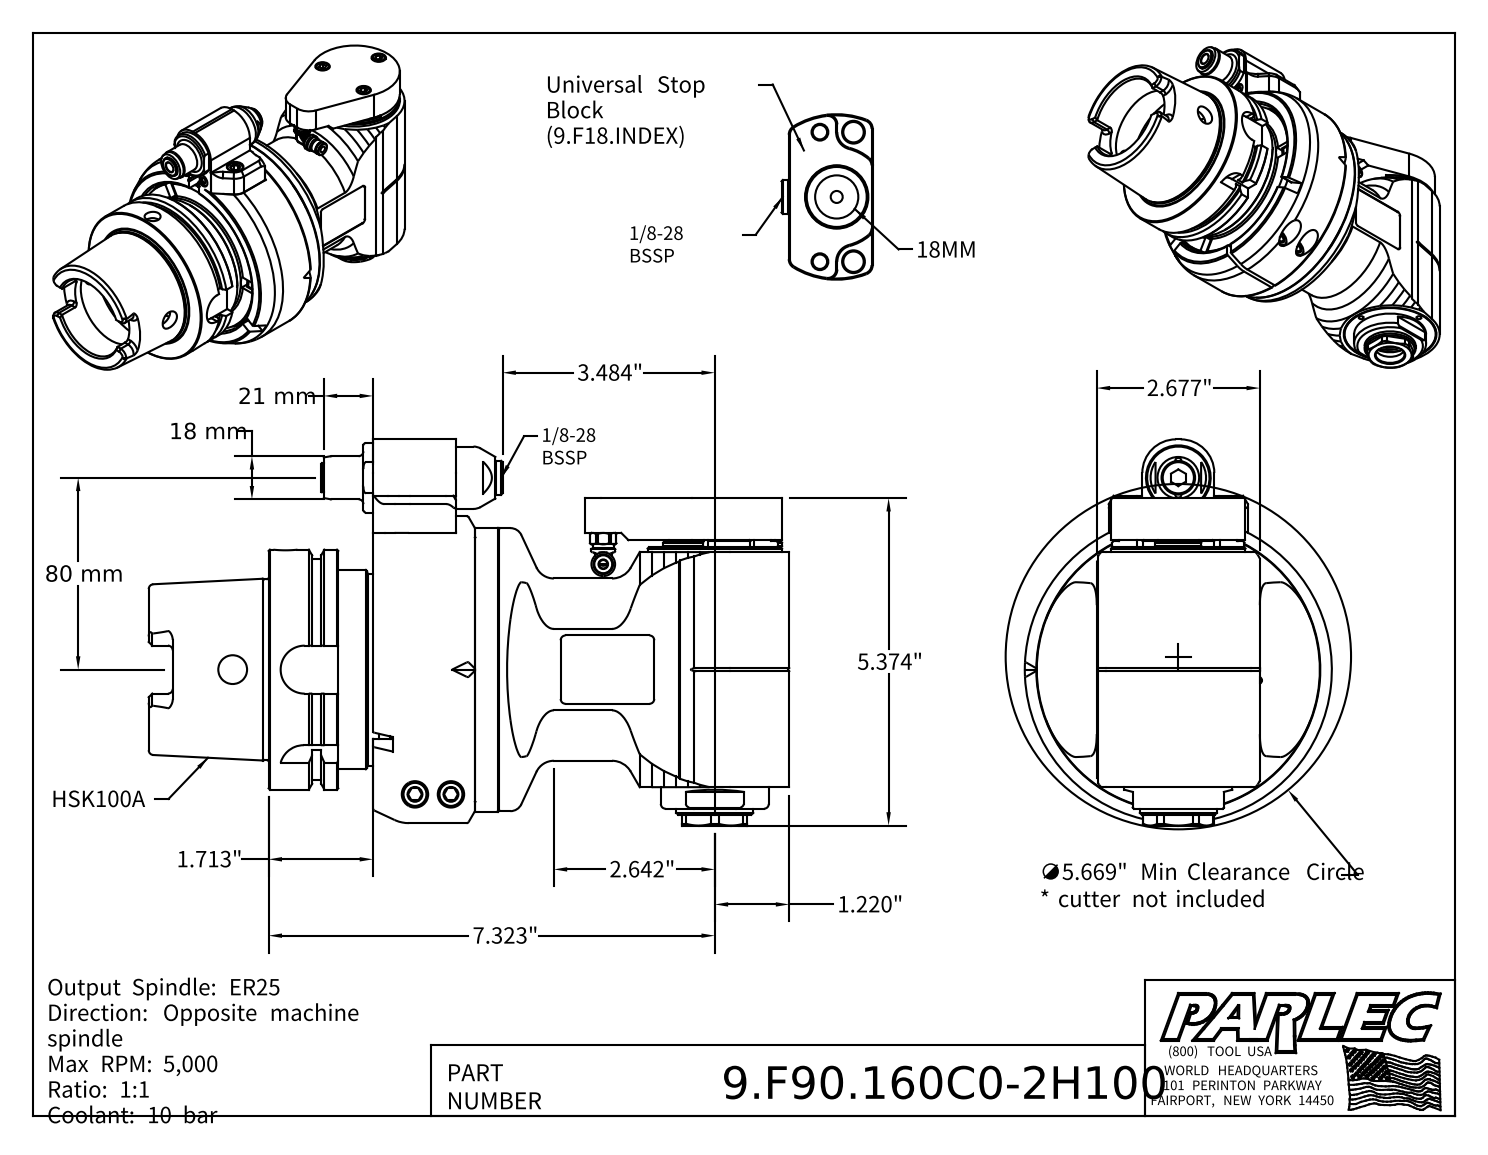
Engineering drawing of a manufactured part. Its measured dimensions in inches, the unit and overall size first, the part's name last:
Units: inches
Overall size (bounding box): 10.512 × 6.339 × 5.039
Round holes (diameter × count): ⌀0.413 ×20, ⌀0.126 ×4, ⌀0.197 ×3, ⌀0.256 ×3, ⌀0.354 ×3, ⌀0.492 ×3, ⌀0.102 ×2, ⌀0.13 ×2, ⌀0.138 ×2, ⌀0.165 ×2, ⌀0.315 ×2, ⌀0.409 ×2
Round bosses / shafts (diameter × count): ⌀0.394 ×5, ⌀0.472 ×3, ⌀0.335 ×3, ⌀0.709 ×2, ⌀0.236 ×2, ⌀0.098 ×2, ⌀5.039 ×1, ⌀4.661 ×1
Partial cylindrical surfaces — rounded edges, fillets, slot ends (radius × count): R0.079 ×19, R0.039 ×18, R0.118 ×6, R0.394 ×6, R0.02 ×4, R0.157 ×4, R0.192 ×4, R0.006 ×3
Main face-to-face distances: 1.378, 0.02, 1.398, 0.197, 0.039, 0.276, 2.047, 0.118, 1.673, 1.339
Hole centre spacings: 1.841, 2.215, 2.603, 3.645, 3.681, 1.785, 3.22, 0.512
Volume: 104.9 in³ · Surface area: 362 in²
Bodies: 7 solids, 918 faces (391 planar, 250 cylindrical, 277 other)
Part name (STEP PRODUCT): 9.F90.160C0-2H100; 9GA21C_518 (Type 2, HSK100 , 80mm); 9_F90_160B0
STEP written by: Autodesk Inventor 2022 (AUTOMOTIVE_DESIGN)
